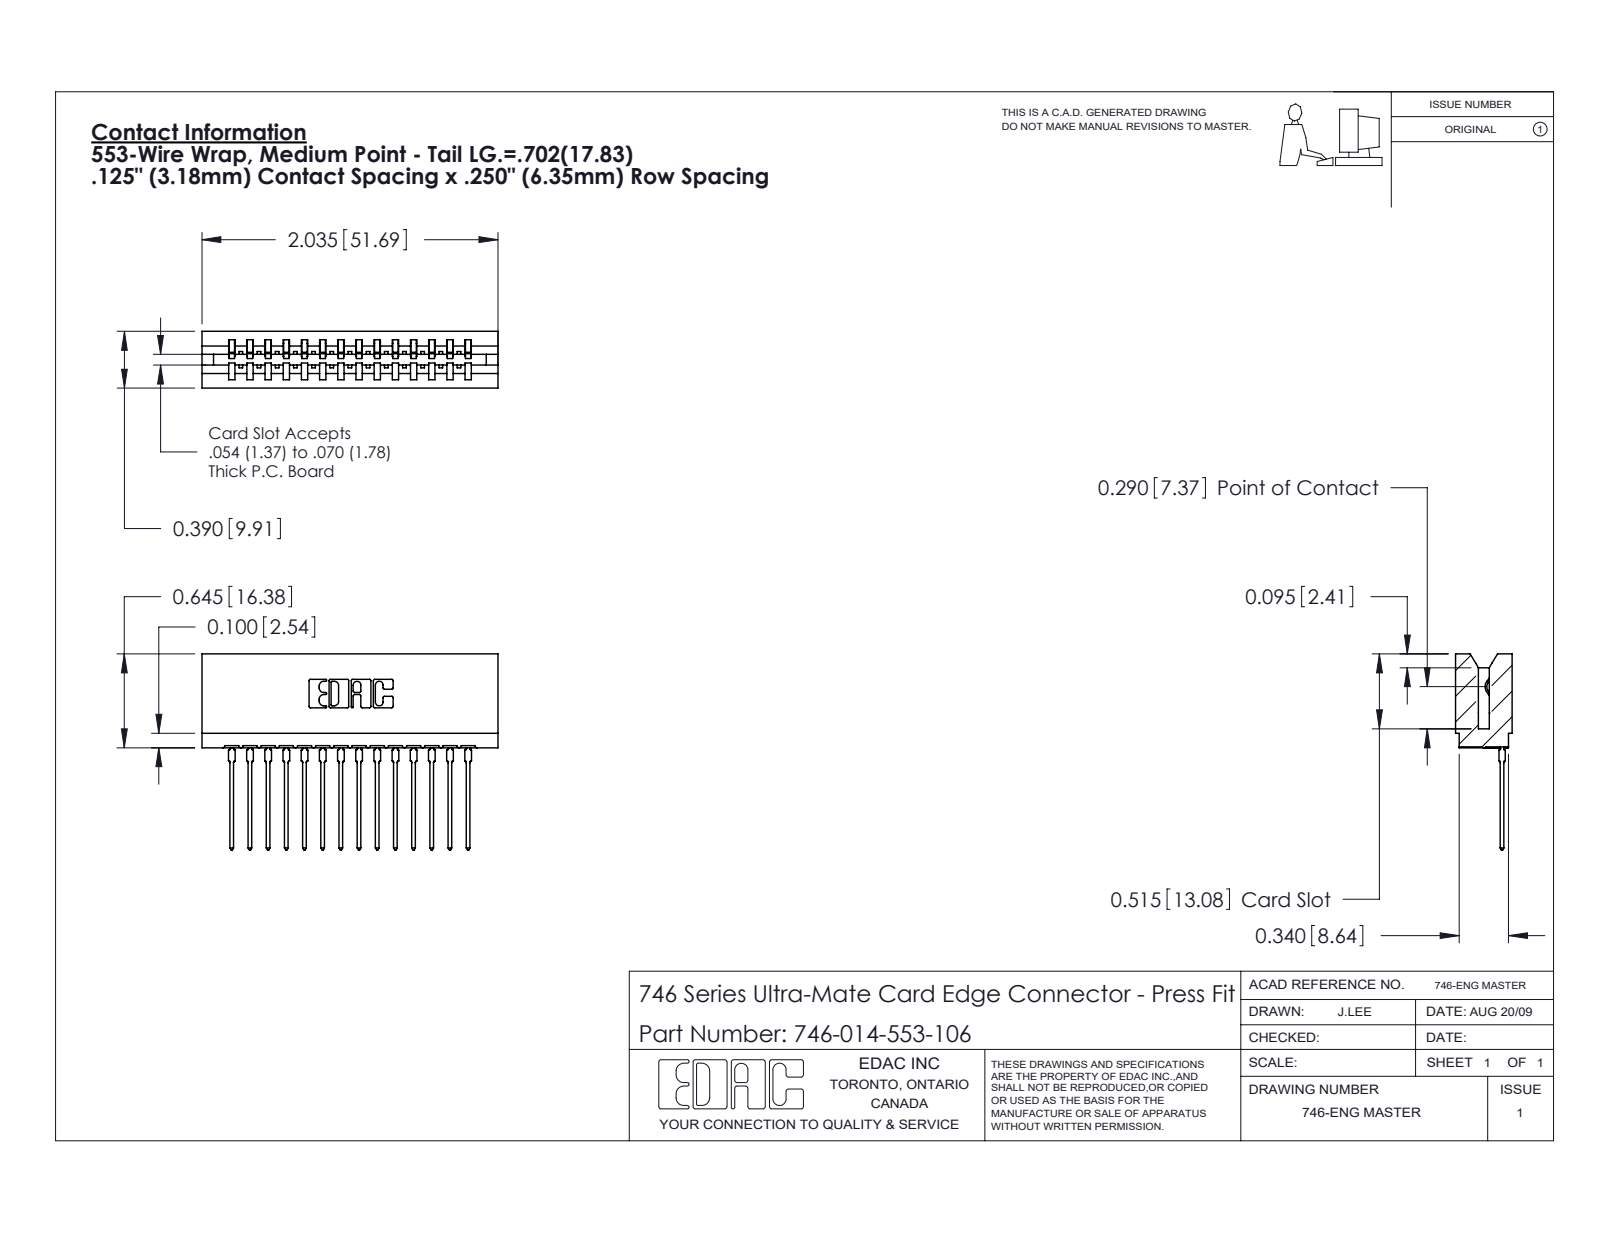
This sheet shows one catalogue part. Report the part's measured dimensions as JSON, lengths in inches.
{"part_name": "746-014-553-106; 746 Part_.515 Slot Depth - 06; 746-292-001_553", "step_written_by": "SolidWorks 2020 (CONFIG_CONTROL_DESIGN)", "units": "inches", "bodies": {"solids": 15, "faces": 1610, "planar": 938, "cylindrical": 308, "other": 364}, "overall_size": [2.035, 1.346, 0.39], "volume_in3": 0.343, "surface_area_in2": 12.61, "partial_cylinders_radius": [[0.021, 28], [0.01, 22], [0.015, 15], [0.007, 6], [0.031, 6], [0.005, 4], [0.011, 4], [0.026, 3]], "face_to_face_distances": [0.25, 0.333, 0.057, 0.5, 0.39, 0.125, 0.083, 0.042, 0.208, 0.375]}
